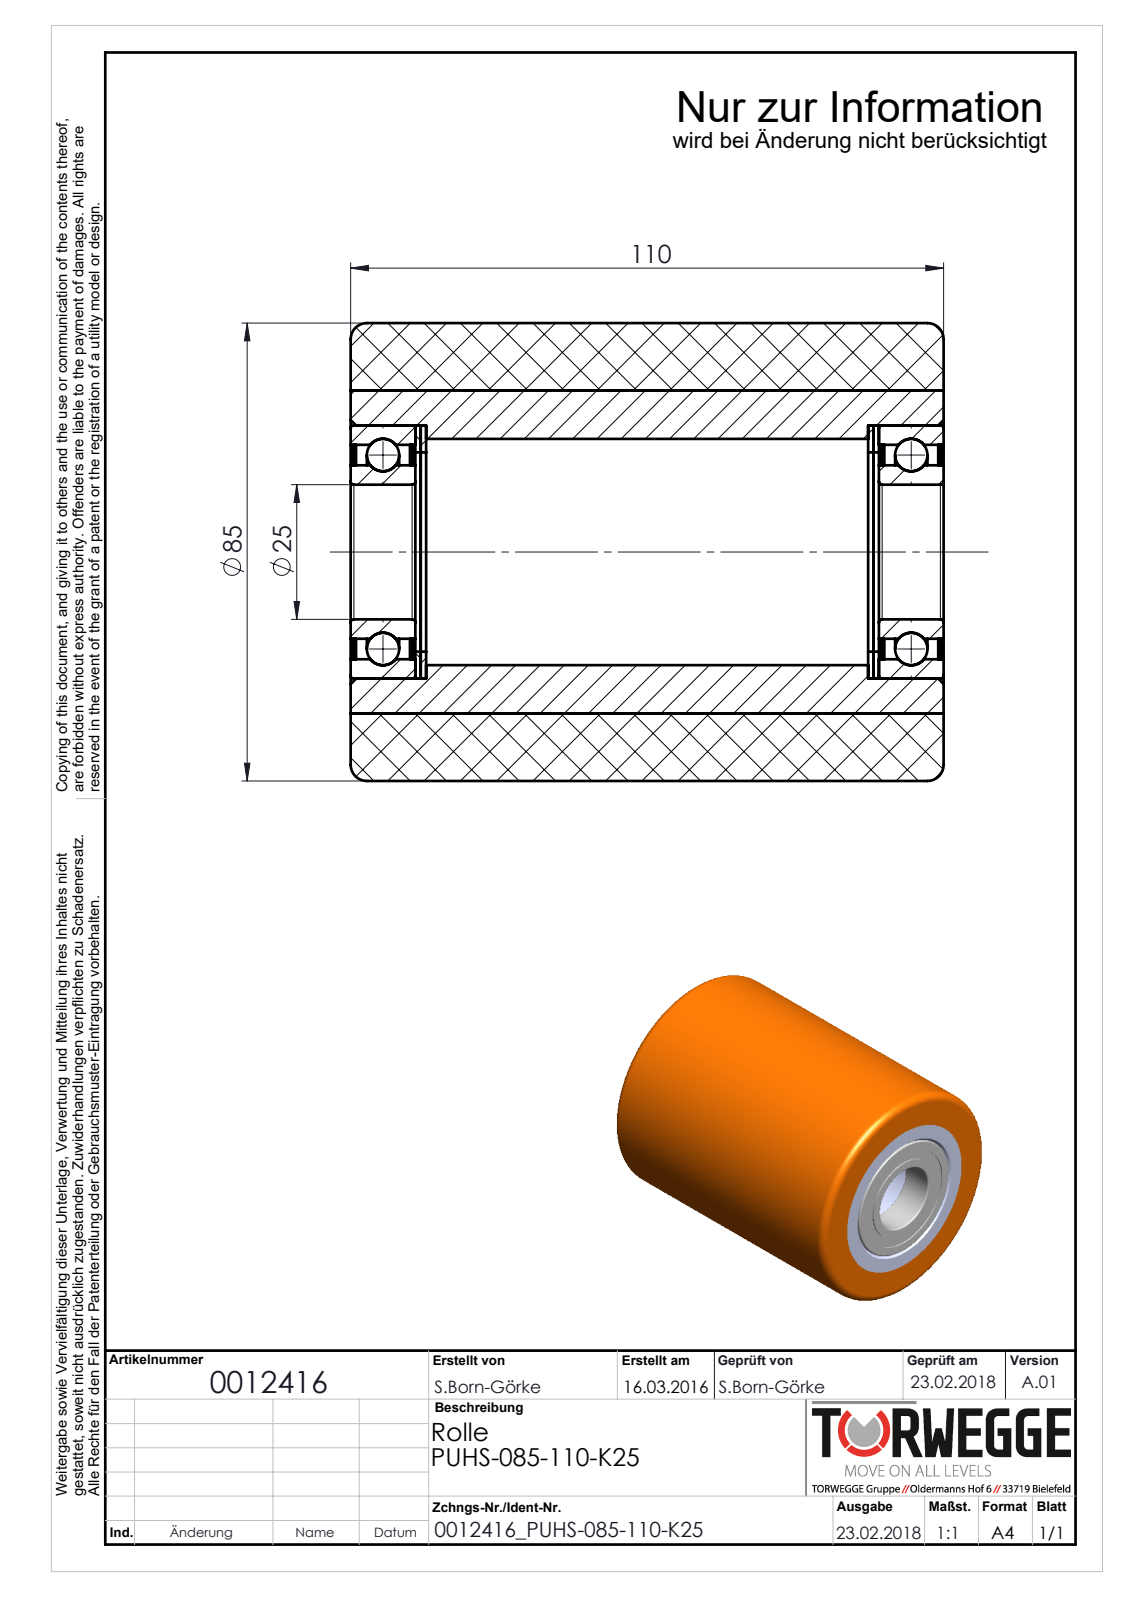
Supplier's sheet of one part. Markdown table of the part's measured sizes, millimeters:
| quantity | value |
| --- | --- |
| part name | 0012416_PUHS-085-110-K25 |
| STEP written by | SolidWorks 2016 (AUTOMOTIVE_DESIGN) |
| units | millimeters |
| bodies | 16 solids, 158 faces (30 planar, 68 cylindrical, 60 other) |
| overall size | 110 × 85 × 85 |
| volume | 488 334 mm³ |
| surface area | 122 078 mm² |
| round holes (diameter × count) | 25 × 1, 32.2 × 1, 37 × 1, 39.8 × 1, 42 × 1, 60 × 1 |
| round bosses / shafts (diameter × count) | 85 × 1, 47 × 1 |
| main face-to-face distances | 1, 98, 110, 12, 0.5, 13, 97, 85, 84, 96 |
